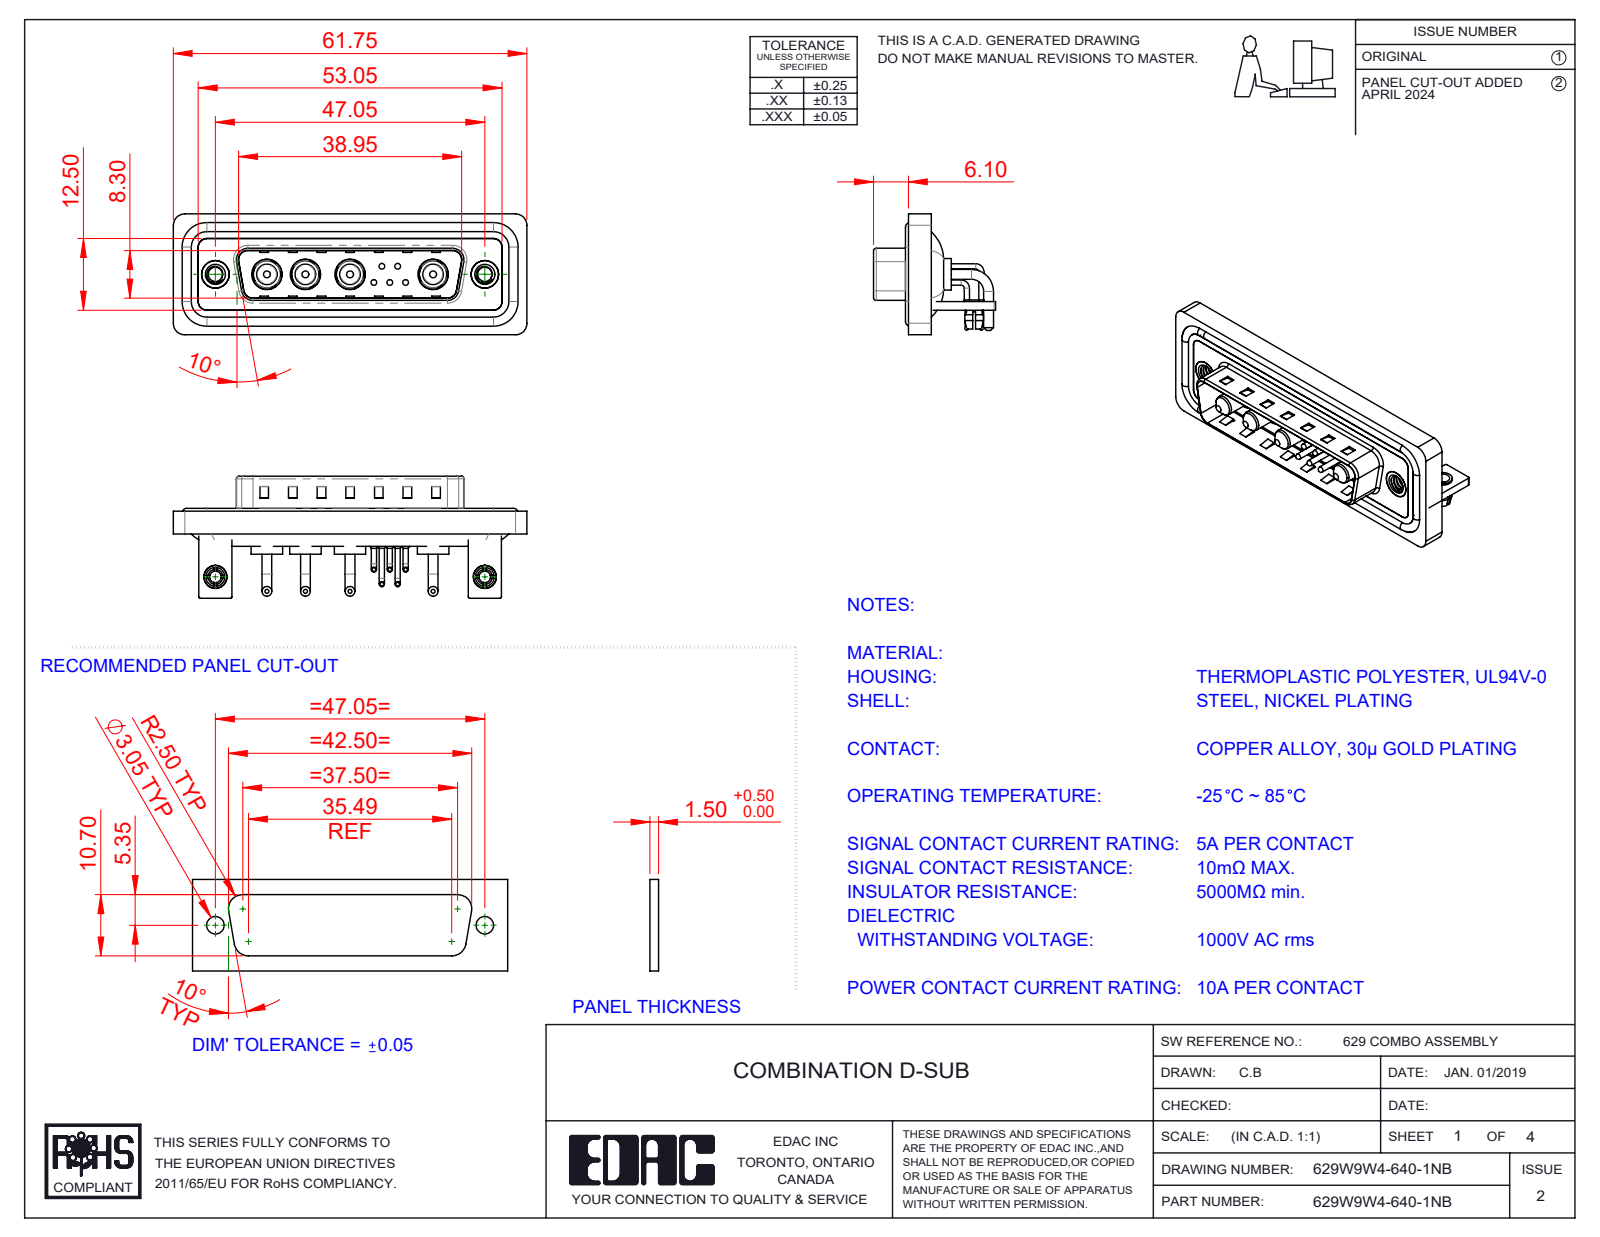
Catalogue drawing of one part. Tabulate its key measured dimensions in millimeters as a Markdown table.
| quantity | value |
| --- | --- |
| part name | 629Combo Threaded Rivet_B; 629W9W4-640-1NB; 629Combo Stabilizer Bracket; Power Pin_10A RA (+7 more) |
| STEP written by | SolidWorks 2023 (CONFIG_CONTROL_DESIGN) |
| units | millimeters |
| bodies | 24 solids, 1335 faces (637 planar, 502 cylindrical, 196 other) |
| overall size | 61.75 × 21.3 × 21.1 |
| volume | 7 780 mm³ |
| surface area | 12 971 mm² |
| round holes (diameter × count) | 2 × 7, 0.75 × 5, 1.6 × 5, 2.5 × 4, 4.85 × 4, 5.3 × 4, 3.2 × 2, 4 × 2, 4.8 × 2, 5 × 2 |
| round bosses / shafts (diameter × count) | 0.9 × 10, 1.7 × 8, 1.5 × 5, 1 × 5, 0.65 × 5, 5.5 × 4, 5.2 × 4, 4.75 × 4 |
| partial cylindrical surfaces (radius × count) | 2 × 19, 1.5 × 18, 0.25 × 16, 0.5 × 9, 1.6 × 8, 1.01 × 5, 0.6 × 4, 0.65 × 4 |
| main face-to-face distances | 0.4, 1.5, 0.8, 2.9, 2.1, 1.1, 3.7, 4.1, 4.5, 1.6 |
| hole center spacings | 3.16, 2.77, 5.04, 14.5, 47.05, 2.78, 4.4, 4.41 |
